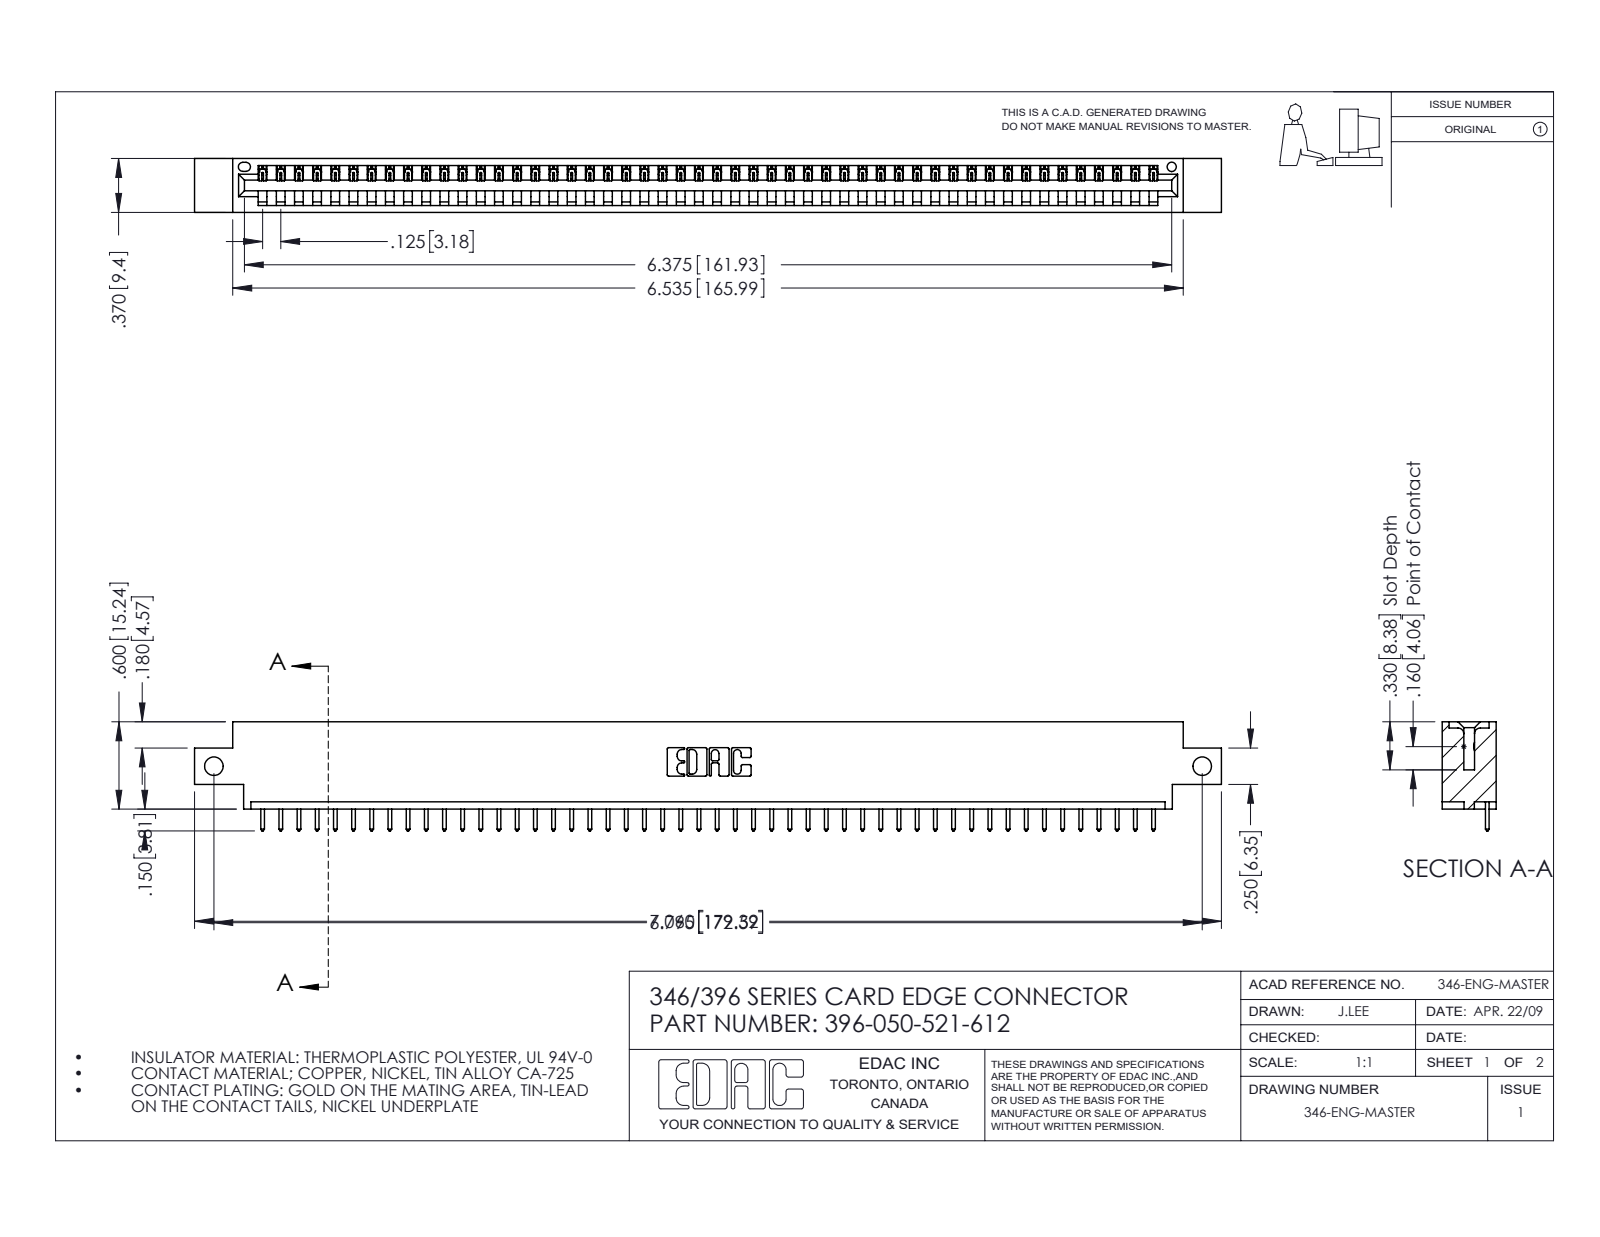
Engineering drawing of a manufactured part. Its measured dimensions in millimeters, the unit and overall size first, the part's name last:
Units: millimetres
Overall size (bounding box): 179.3 × 19.1 × 9.4
Round holes (diameter × count): ⌀3.3 ×2, ⌀1.6 ×1
Partial cylindrical surfaces — rounded edges, fillets, slot ends (radius × count): R0.2 ×100, R0.3 ×100, R0.3 ×22, R0.2 ×6, R0.8 ×6, R0.7 ×3, R0.8 ×2, R1 ×2
Main face-to-face distances: 1.2, 8.2, 9.4, 6.4, 1.8, 7.6, 0.6, 3.8, 5.6, 2.5
Hole centre spacings: 172.6
Volume: 16 830 mm³ · Surface area: 20 580 mm²
Bodies: 51 solids, 3026 faces (2080 planar, 946 cylindrical, 0 other)
Part name (STEP PRODUCT): 345-292-001_345-293-121; 346 Part_0.170 Offset - Side Mount; 396-050-521-612
STEP written by: SolidWorks 2016 (CONFIG_CONTROL_DESIGN)
